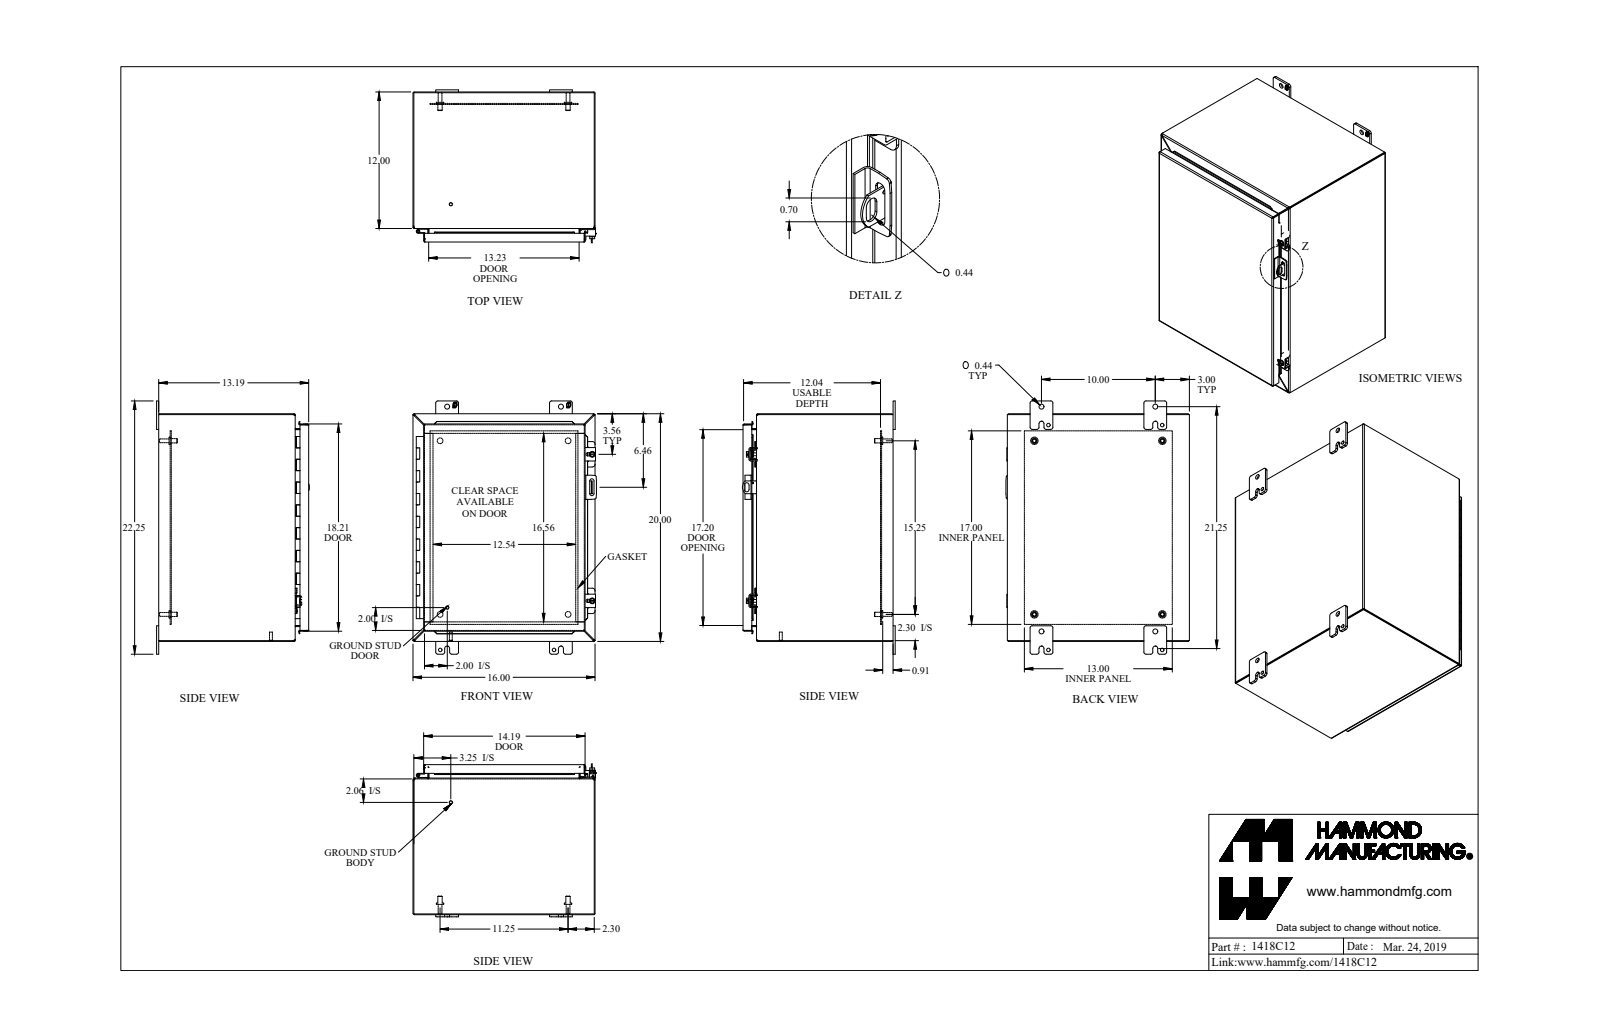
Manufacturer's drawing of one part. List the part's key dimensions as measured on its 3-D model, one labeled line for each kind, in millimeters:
Part name (STEP PRODUCT): 1418C12
STEP written by: SolidWorks 2019 (AUTOMOTIVE_DESIGN)
Units: millimetres
Bodies: 40 solids, 966 faces (651 planar, 255 cylindrical, 60 other)
Overall size (bounding box): 565.2 × 409.6 × 341.3
Volume: 2 561 000 mm³ · Surface area: 2 653 000 mm²
Round holes (diameter × count): ⌀8 ×4, ⌀11.1 ×4, ⌀12.7 ×4, ⌀5.4 ×2, ⌀6.7 ×2, ⌀7.8 ×2, ⌀9.5 ×2, ⌀11.3 ×2, ⌀3.2 ×1, ⌀4.7 ×1
Round bosses / shafts (diameter × count): ⌀16.5 ×4, ⌀9.5 ×4, ⌀8.4 ×4, ⌀25.4 ×2, ⌀12.7 ×2, ⌀9.9 ×2, ⌀7.1 ×2, ⌀6.4 ×2
Partial cylindrical surfaces — rounded edges, fillets, slot ends (radius × count): R4.8 ×26, R0.9 ×18, R2.7 ×18, R1.2 ×13, R3.6 ×13, R6.4 ×12, R0.2 ×8, R1 ×8
Main face-to-face distances: 1.8, 333.1, 404.6, 506.2, 331.2, 23.8, 334.9, 25.6, 402.7, 406.4
Hole centre spacings: 254, 481.4, 44.1, 77.9, 272.5, 285.8, 425.8, 501.7
